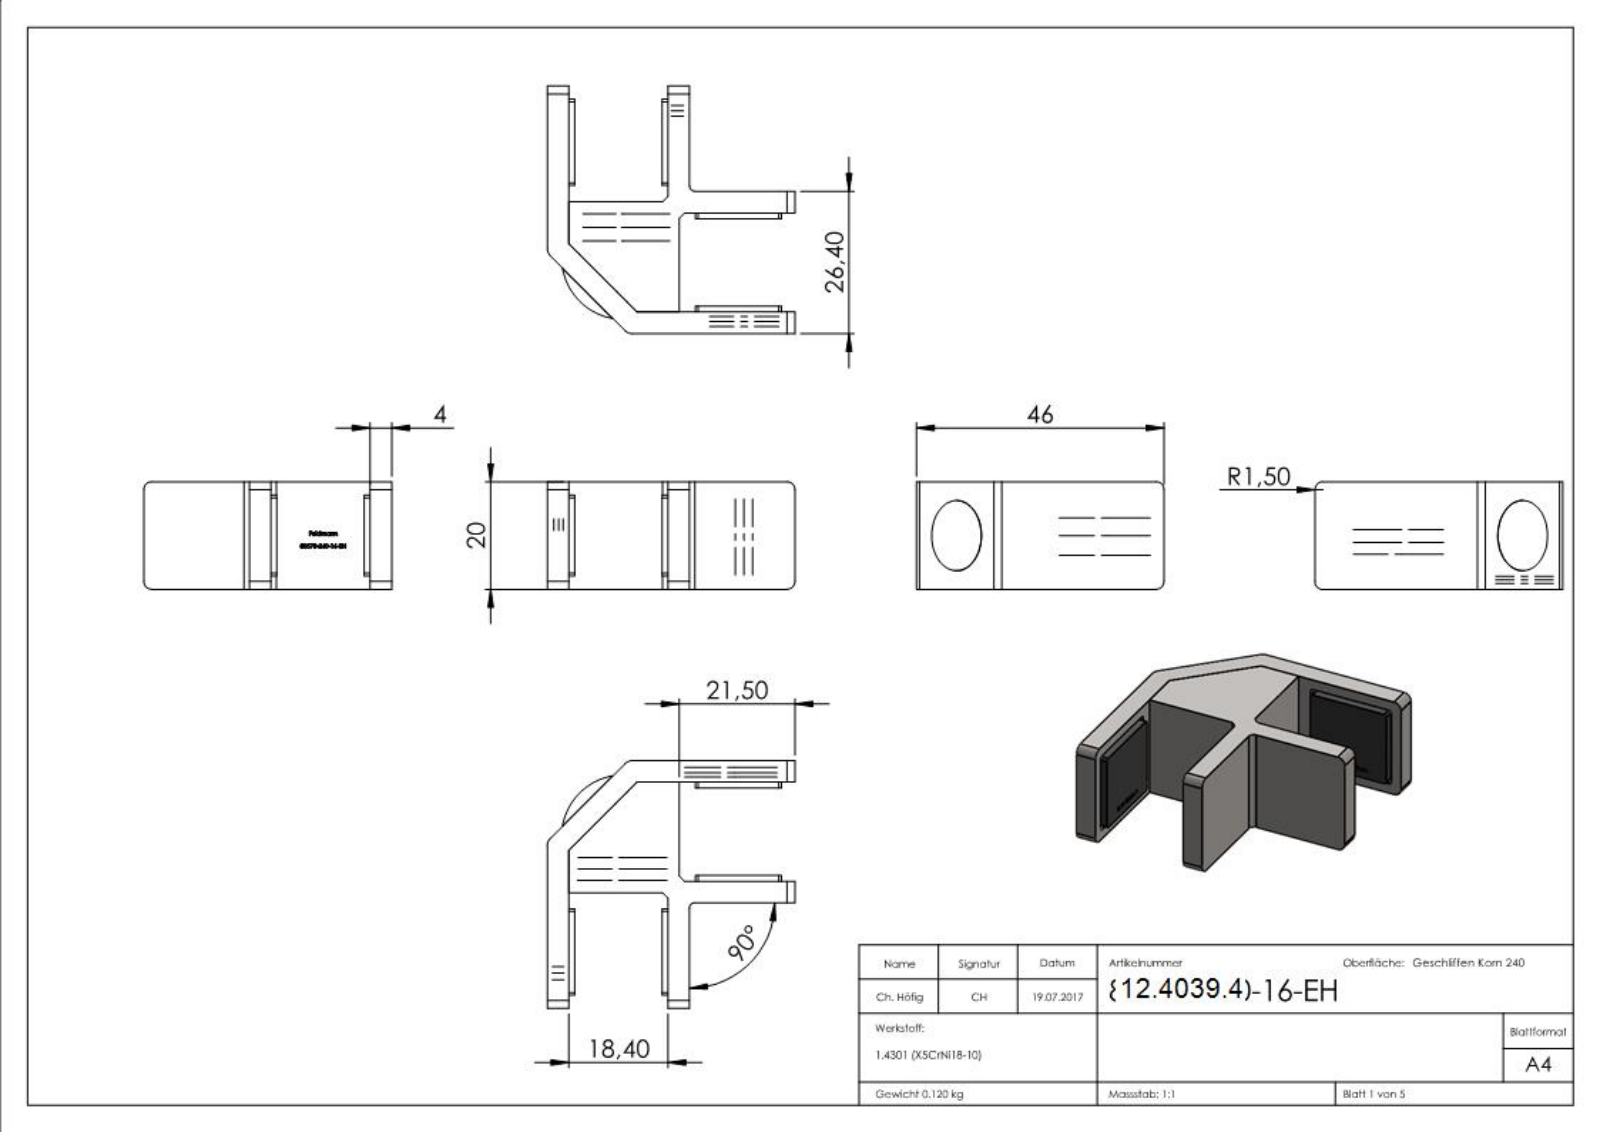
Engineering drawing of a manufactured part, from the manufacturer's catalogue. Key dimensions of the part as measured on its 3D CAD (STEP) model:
Part name (STEP PRODUCT): 80570-240-16-EH; 80570-xxx-xx-EH Teil1_80570-240-16-EH Teil1; 80570-xxx-xx-EH Teil3; socket countersunk head screw_din_DIN 7991 - M6 x 16 --- 16S (+6 more)
STEP written by: SolidWorks 2018 (CONFIG_CONTROL_DESIGN)
Units: millimetres
Bodies: 8 solids, 2838 faces (1625 planar, 209 cylindrical, 1004 other)
Overall size (bounding box): 46 × 46 × 20
Volume: 17 306 mm³ · Surface area: 12 396 mm²
Round holes (diameter × count): ⌀2.7 ×2, ⌀1.8 ×1, ⌀5 ×1, ⌀7 ×1, ⌀12.5 ×1
Round bosses / shafts (diameter × count): ⌀11.57 ×1, ⌀6 ×1, ⌀4 ×1
Partial cylindrical surfaces — rounded edges, fillets, slot ends (radius × count): R0.2 ×56, R0.5 ×48, R1.5 ×4, R2 ×2, R1 ×1
Main face-to-face distances: 4, 3.5, 1.6, 0.5, 22.9, 22.4, 19.4, 5.1, 18.9, 21.3
Hole centre spacings: 8.2, 16.4
